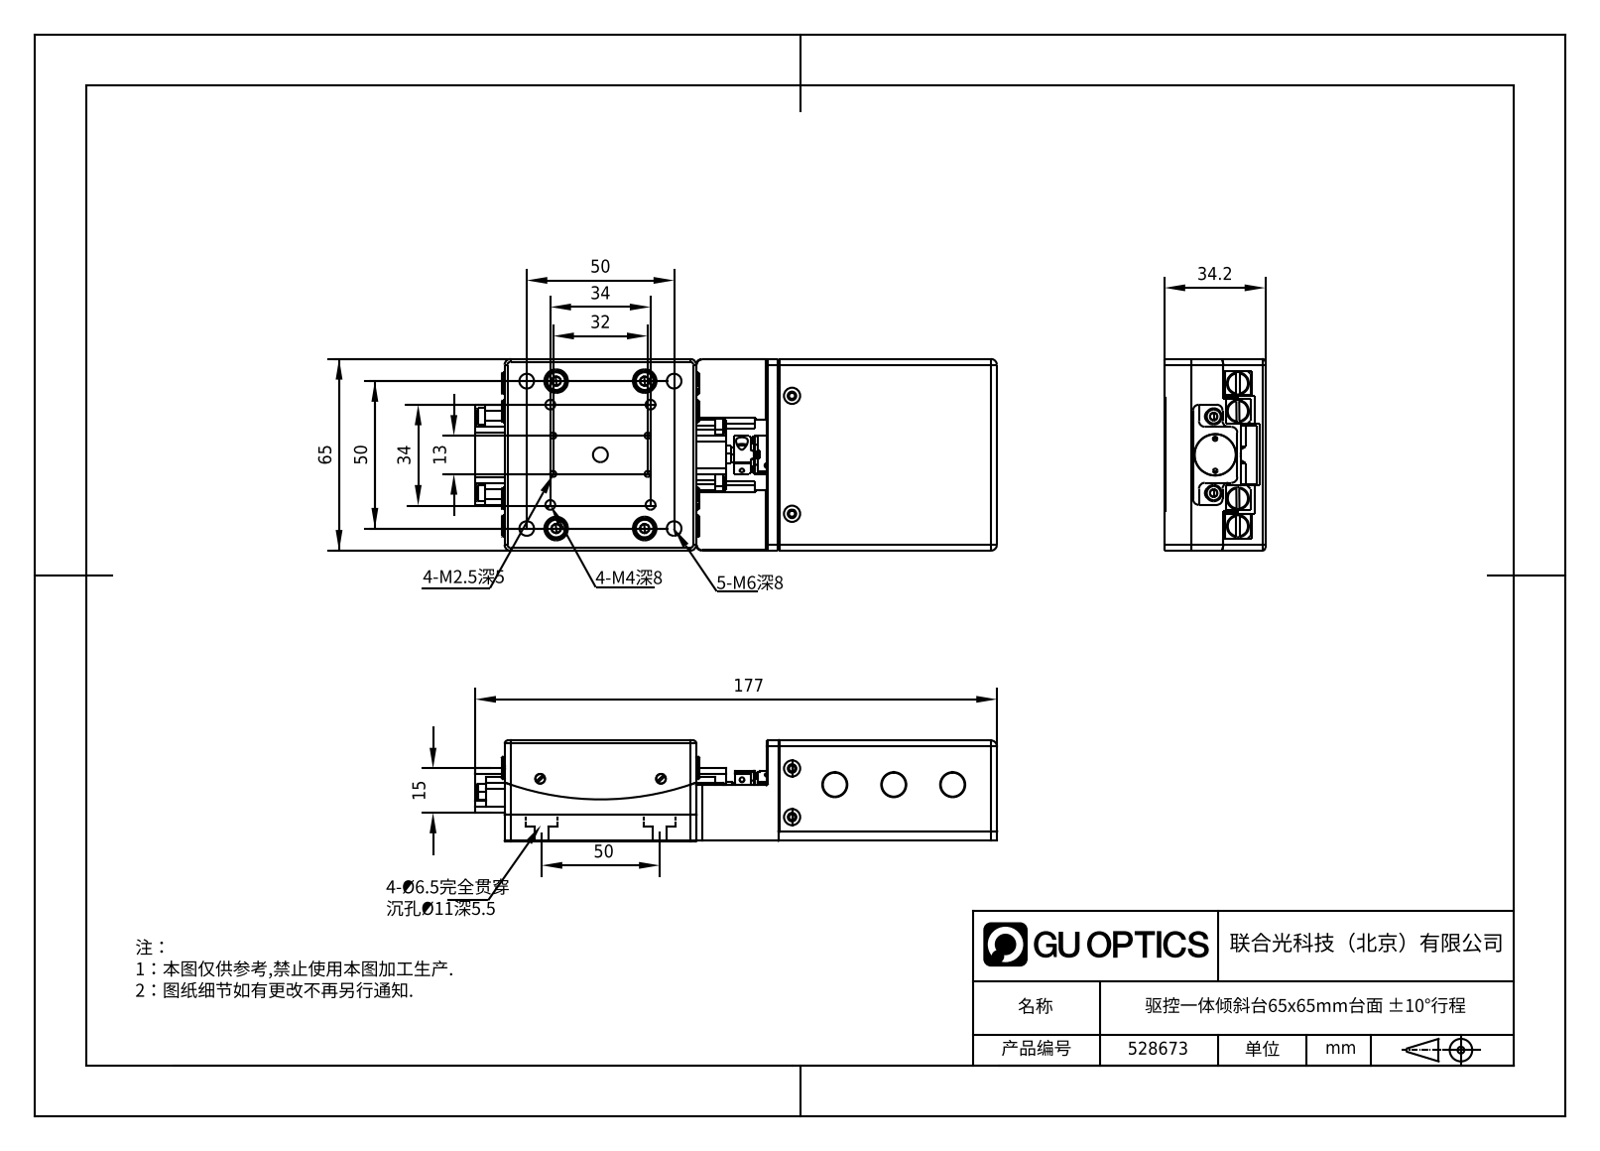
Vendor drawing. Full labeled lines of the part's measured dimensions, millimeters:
Part name (STEP PRODUCT): 528673
STEP written by: SolidWorks 2020 (CONFIG_CONTROL_DESIGN)
Units: millimetres
Bodies: 55 solids, 1693 faces (678 planar, 654 cylindrical, 361 other)
Overall size (bounding box): 177 × 65 × 34.2
Volume: 250 924 mm³ · Surface area: 126 011 mm²
Round holes (diameter × count): ⌀3.3 ×14, ⌀2.05 ×12, ⌀5 ×12, ⌀2.5 ×10, ⌀2.9 ×8, ⌀4.5 ×8, ⌀3.2 ×6, ⌀11 ×6, ⌀2 ×5, ⌀3 ×5, ⌀5.5 ×4, ⌀6.5 ×4
Round bosses / shafts (diameter × count): ⌀4 ×10, ⌀7 ×8, ⌀3 ×8, ⌀7.5 ×4, ⌀5.5 ×4, ⌀2.5 ×4, ⌀2.4 ×4, ⌀2.2 ×4
Partial cylindrical surfaces — rounded edges, fillets, slot ends (radius × count): R2 ×43, R3 ×6, R1 ×4, R1.35 ×4, R6.45 ×1, R83.5 ×1, R85 ×1, R86 ×1
Main face-to-face distances: 3, 31, 25, 6, 9, 65, 2.5, 34, 4, 22.5
Hole centre spacings: 20.52, 42.76, 20.11, 7.57, 10, 13.21, 24.04, 39
